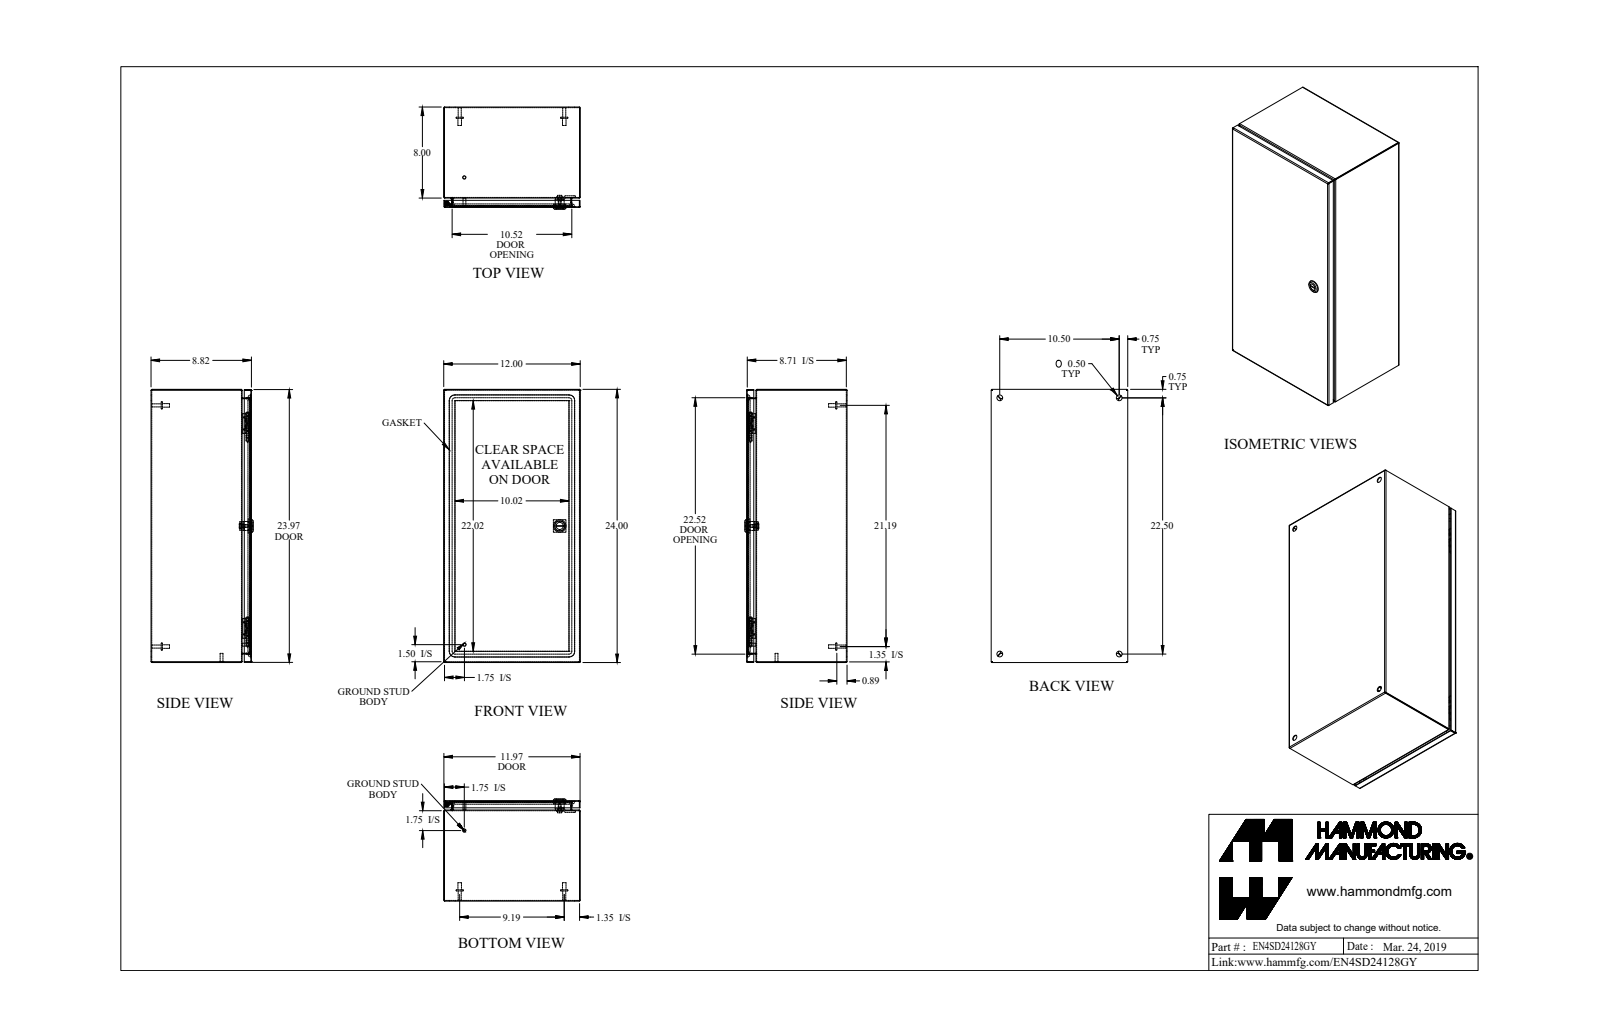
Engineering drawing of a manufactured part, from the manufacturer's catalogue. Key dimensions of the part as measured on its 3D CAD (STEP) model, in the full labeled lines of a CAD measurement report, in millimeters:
Part name (STEP PRODUCT): EN4SD24128GY_Default
STEP written by: SolidWorks 2019 (CONFIG_CONTROL_DESIGN)
Units: millimetres
Bodies: 21 solids, 634 faces (285 planar, 213 cylindrical, 136 other)
Overall size (bounding box): 609.6 × 304.8 × 228.1
Volume: 1 324 000 mm³ · Surface area: 1 770 000 mm²
Round holes (diameter × count): ⌀12.7 ×4, ⌀4.4 ×1, ⌀5.9 ×1, ⌀6.1 ×1, ⌀6.1 ×1, ⌀15.9 ×1, ⌀19.9 ×1
Round bosses / shafts (diameter × count): ⌀15.9 ×4, ⌀8 ×4, ⌀6.9 ×4, ⌀7.1 ×2, ⌀6.4 ×2, ⌀27.9 ×1, ⌀13.3 ×1, ⌀11.6 ×1
Partial cylindrical surfaces — rounded edges, fillets, slot ends (radius × count): R0.7 ×21, R2.2 ×21, R6.4 ×16, R482.6 ×8, R0.2 ×4, R1.6 ×4, R12.7 ×4, R3.2 ×2
Main face-to-face distances: 1.4, 222.6, 303.4, 221.2, 224.1, 301.9, 304.8, 608.2, 606.7, 609.6
Hole centre spacings: 266.7, 571.5, 630.7, 287, 287, 373, 373
